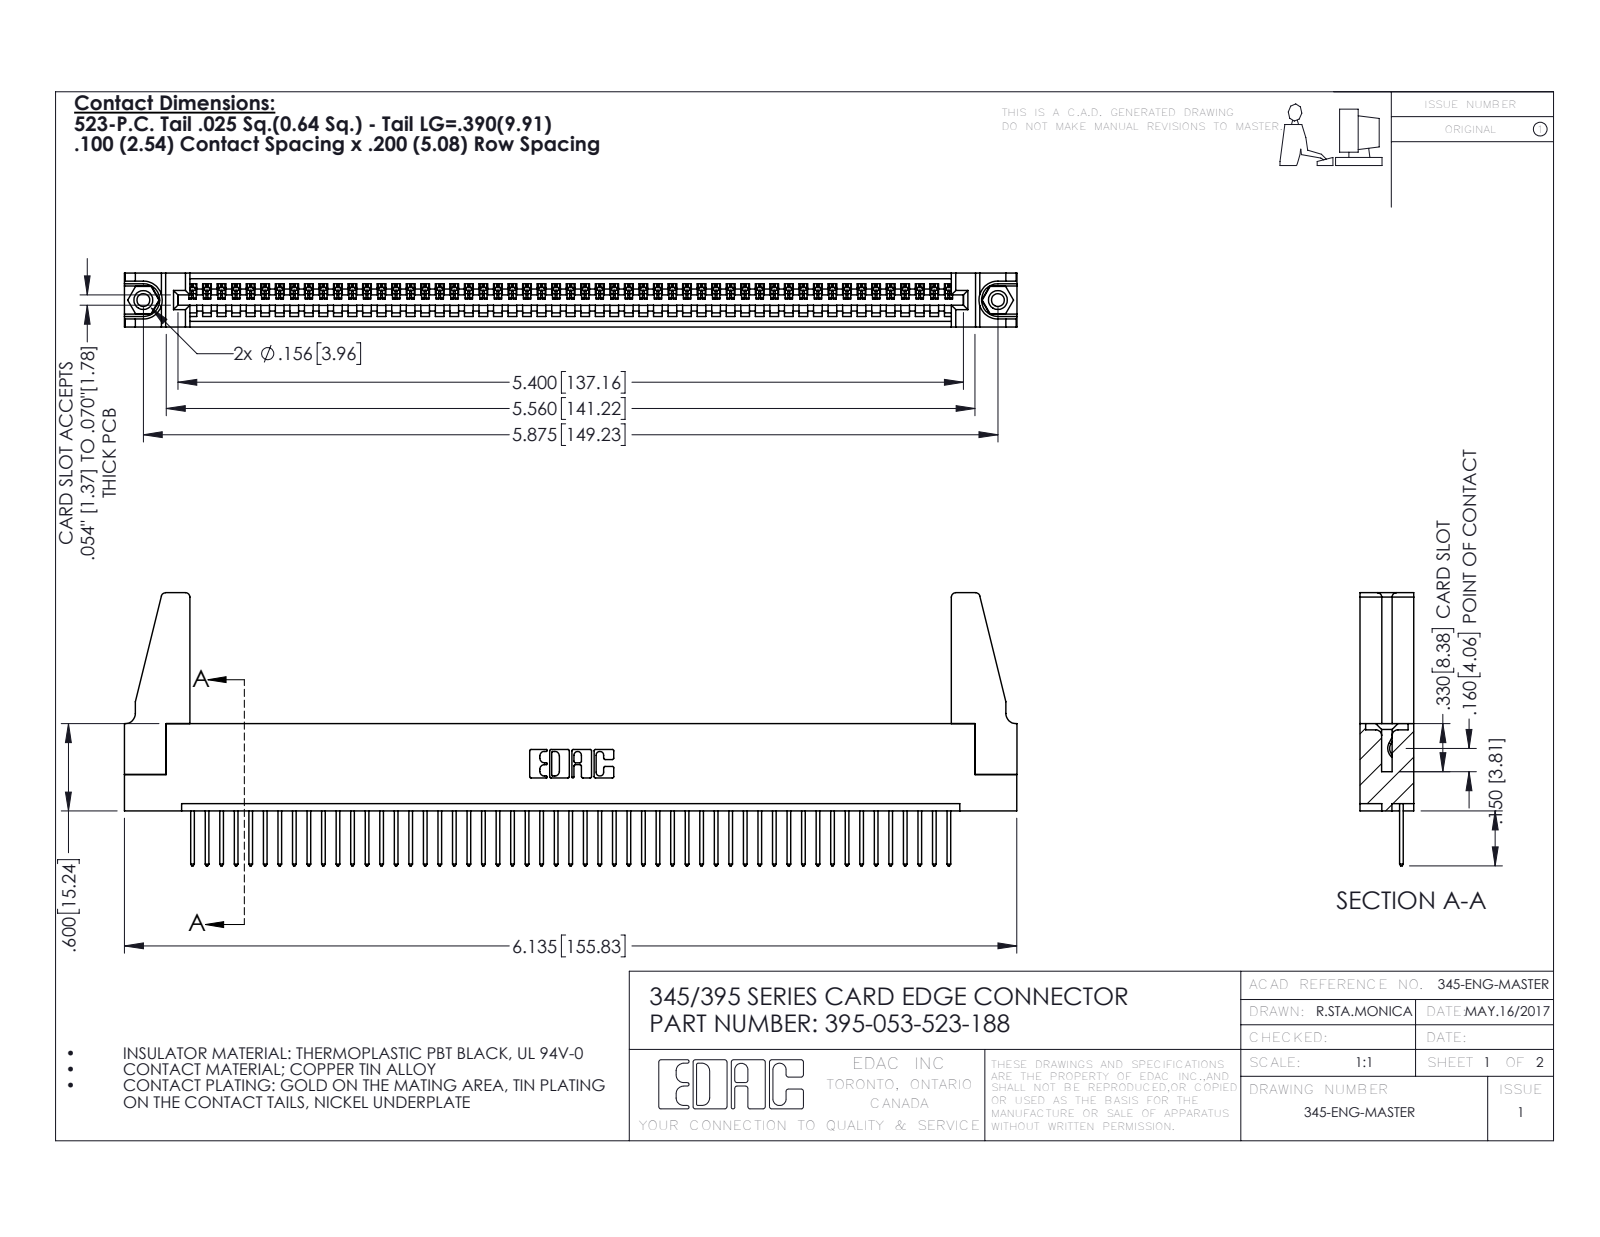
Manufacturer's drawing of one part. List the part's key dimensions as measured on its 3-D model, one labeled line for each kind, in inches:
Part name (STEP PRODUCT): 395-053-523-188; 345-220-078_345-220-088; 345-292-001_345-293-123; 345 Part_Flush Mounting Lugs - 0.156 Dia-TH (+1 more)
STEP written by: SolidWorks 2016 (CONFIG_CONTROL_DESIGN)
Units: inches
Bodies: 58 solids, 3324 faces (2272 planar, 1036 cylindrical, 16 other)
Overall size (bounding box): 6.136 × 1.877 × 0.37
Volume: 1.106 in³ · Surface area: 35.81 in²
Round holes (diameter × count): ⌀0.089 ×2, ⌀0.125 ×2, ⌀0.156 ×2, ⌀0.064 ×1
Round bosses / shafts (diameter × count): ⌀0.155 ×2
Partial cylindrical surfaces — rounded edges, fillets, slot ends (radius × count): R0.006 ×106, R0.01 ×106, R0.01 ×22, R0.03 ×8, R0.007 ×6, R0.031 ×6, R0.026 ×3, R0.031 ×2
Main face-to-face distances: 0.072, 0.298, 0.37, 0.2, 0.098, 0.272, 0.025, 0.225, 0.149, 0.072
Hole centre spacings: 0.27, 5.639, 5.875
